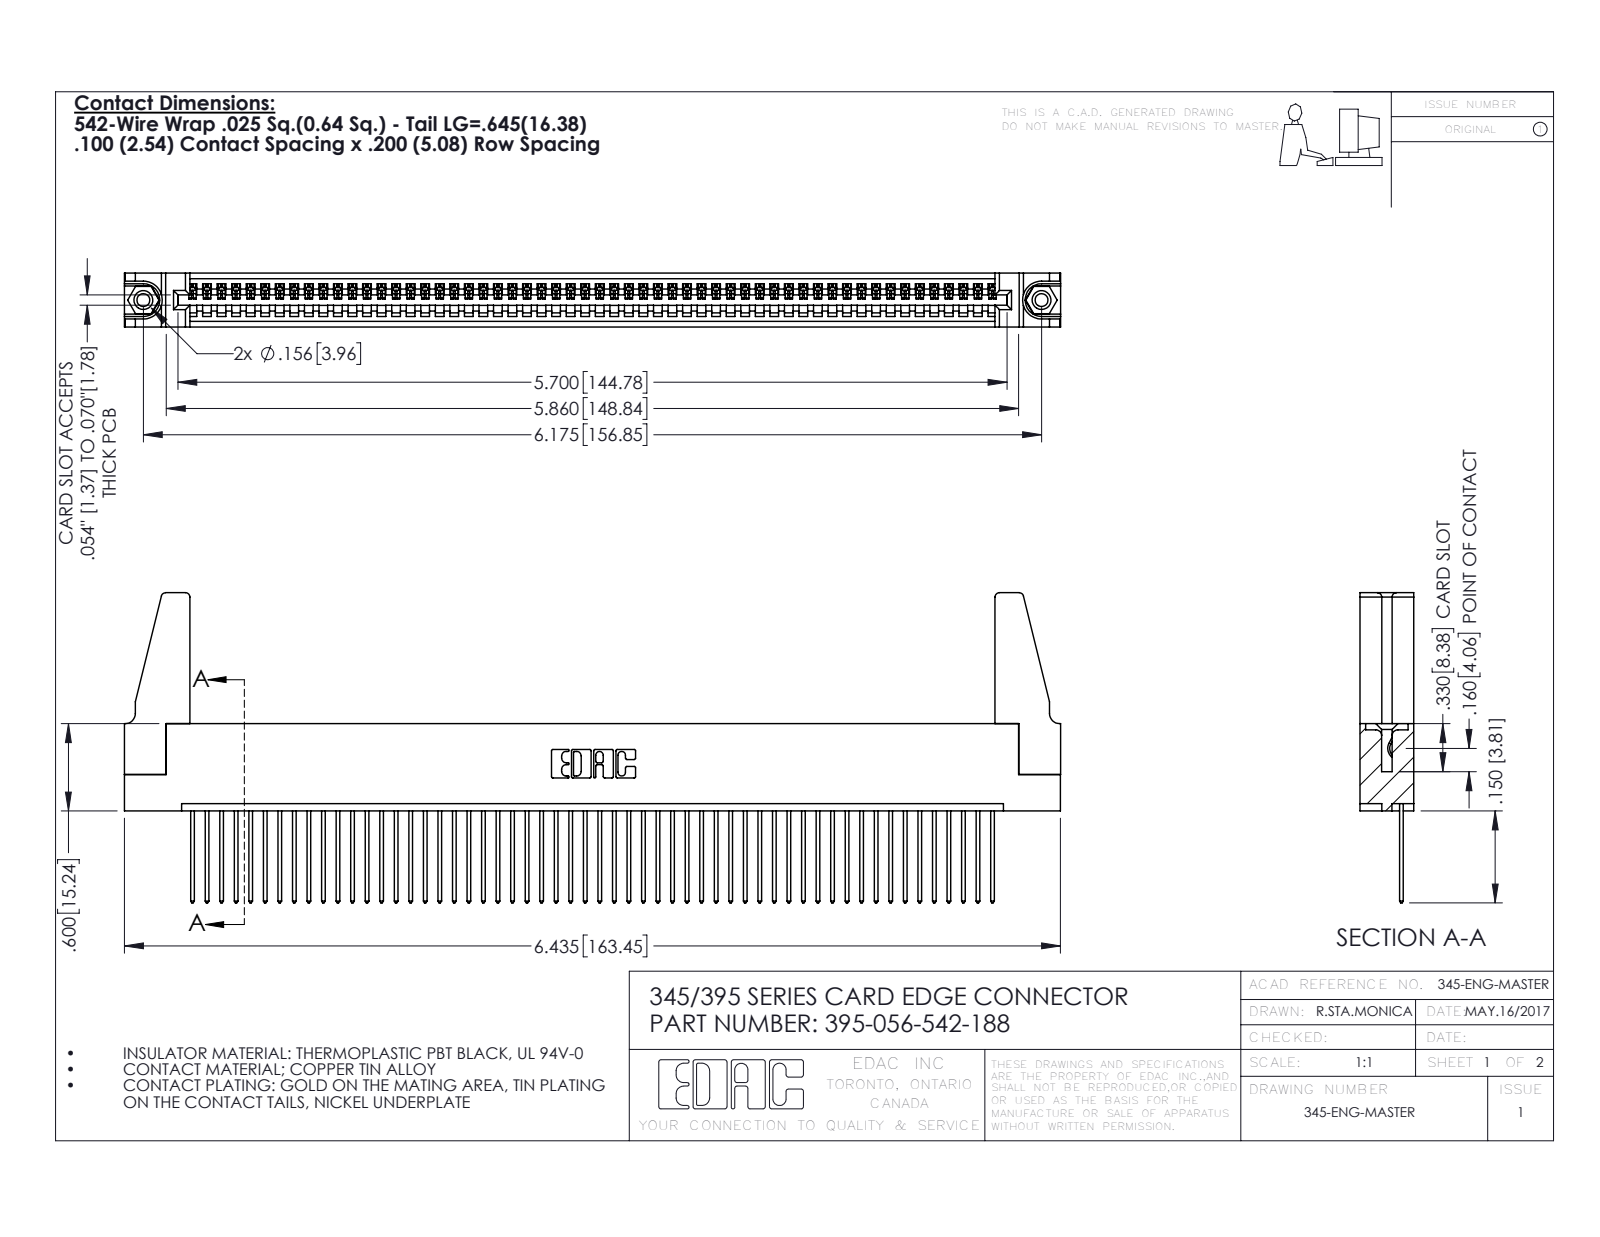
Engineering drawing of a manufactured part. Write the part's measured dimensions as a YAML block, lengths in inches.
part_name: "395-056-542-188; 345-292-001_345-293-142; 345-220-078_345-220-088; 345 Part_Flush Mounting Lugs - 0.156 Dia-TH (+1 more)"
step_written_by: "SolidWorks 2016 (CONFIG_CONTROL_DESIGN)"
units: inches
bodies: {solids: 61, faces: 3498, planar: 2392, cylindrical: 1090, other: 16}
overall_size: [6.436, 2.132, 0.37]
volume: 1.161
surface_area: 38.84
round_holes:
  - {diameter: 0.089, count: 2}
  - {diameter: 0.125, count: 2}
  - {diameter: 0.156, count: 2}
  - {diameter: 0.064, count: 1}
round_bosses_or_shafts:
  - {diameter: 0.155, count: 2}
partial_cylinders:
  - {radius: 0.006, count: 112}
  - {radius: 0.01, count: 112}
  - {radius: 0.01, count: 22}
  - {radius: 0.03, count: 8}
  - {radius: 0.007, count: 6}
  - {radius: 0.031, count: 6}
  - {radius: 0.026, count: 3}
  - {radius: 0.031, count: 2}
face_to_face_distances: [0.072, 0.298, 0.37, 0.098, 0.272, 0.025, 0.2, 0.225, 0.149, 0.072]
hole_center_spacings: [0.27, 5.939, 6.175]
